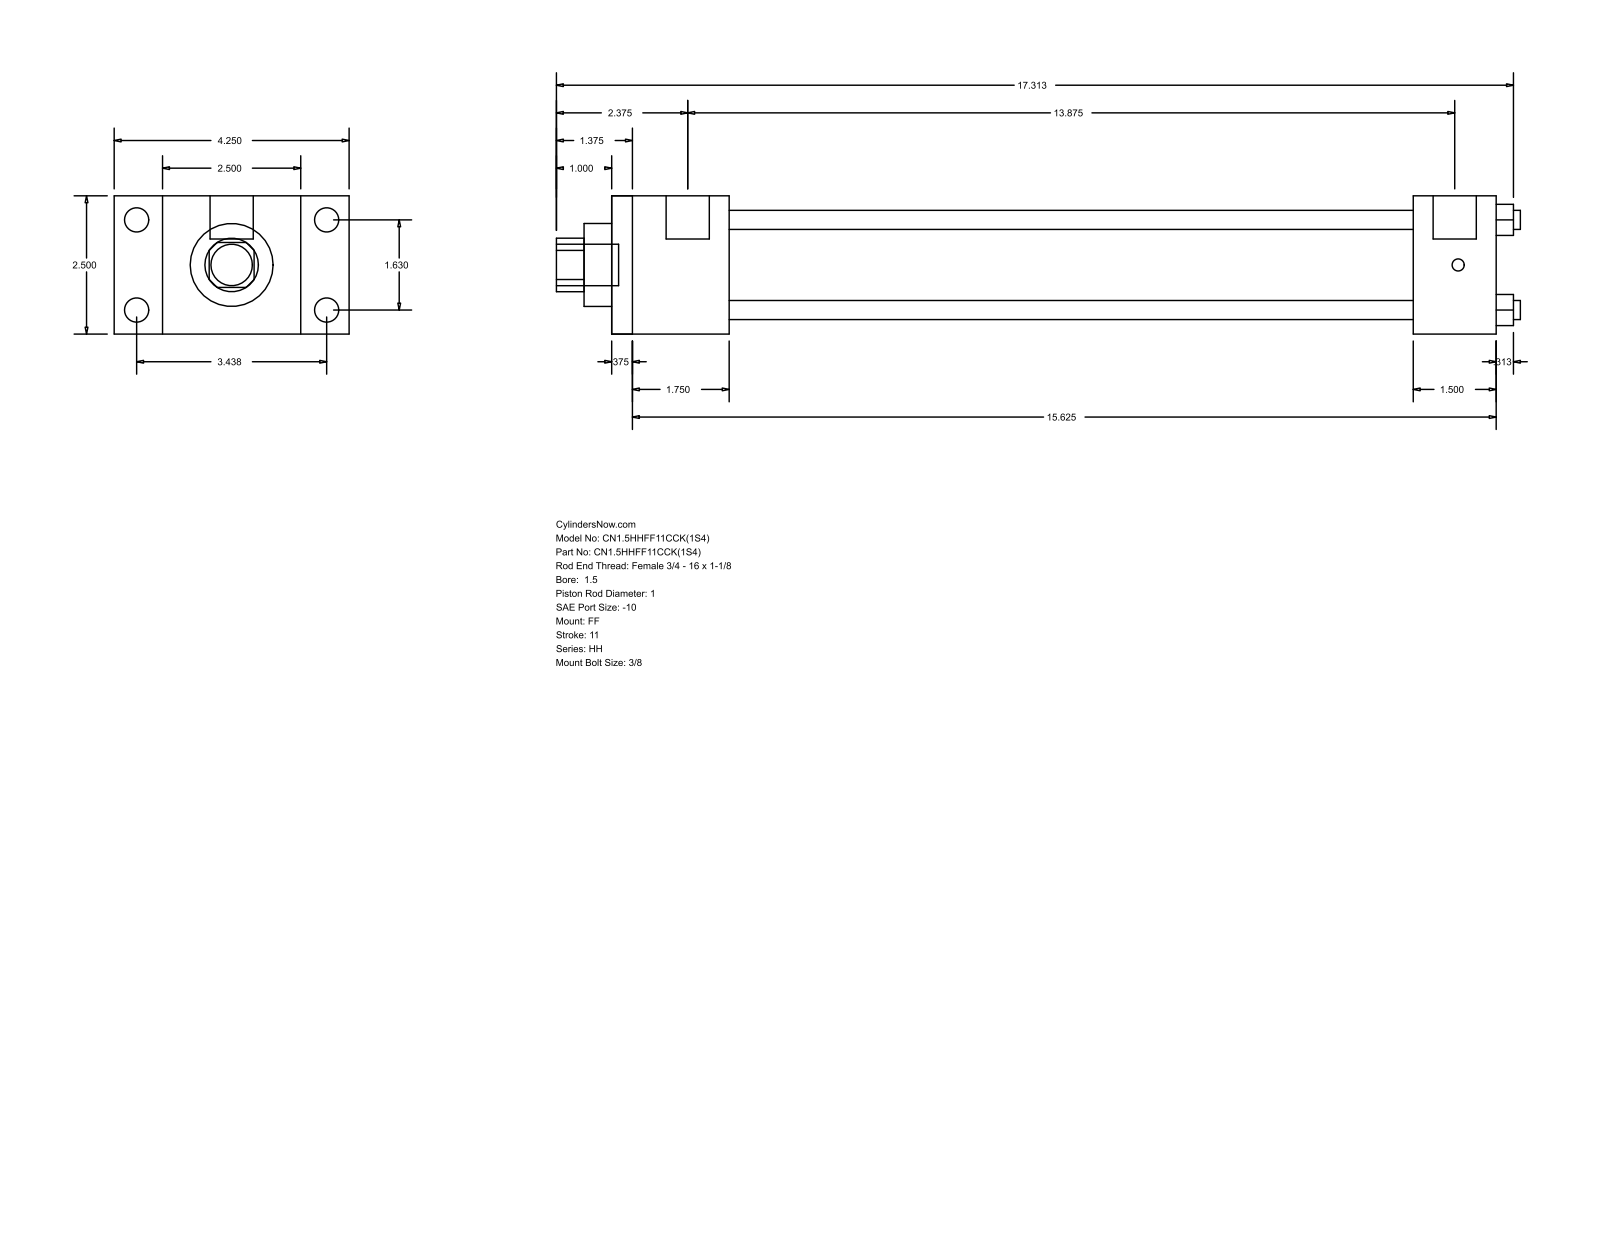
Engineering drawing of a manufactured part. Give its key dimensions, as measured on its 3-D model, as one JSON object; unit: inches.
{"part_name": "HH_FF__0150_1", "step_written_by": "GSSL Pune (CONFIG_CONTROL_DESIGN)", "units": "inches", "bodies": {"solids": 0, "faces": 92, "planar": 64, "cylindrical": 28, "other": 0}, "overall_size": [17.437, 4.25, 2.5], "round_holes": [[0.345, 4], [1, 1], [1.5, 1], [1.75, 1]], "round_bosses_or_shafts": [[0.438, 4], [0.219, 4], [0.781, 2], [0.75, 1]], "partial_cylinders_radius": [[0.484, 1]], "face_to_face_distances": [2.5, 16, 0.375, 15.625, 2.125, 1.75, 13.875, 14.5, 14.125, 12.375], "hole_center_spacings": [1.152, 1.63, 2.305]}
